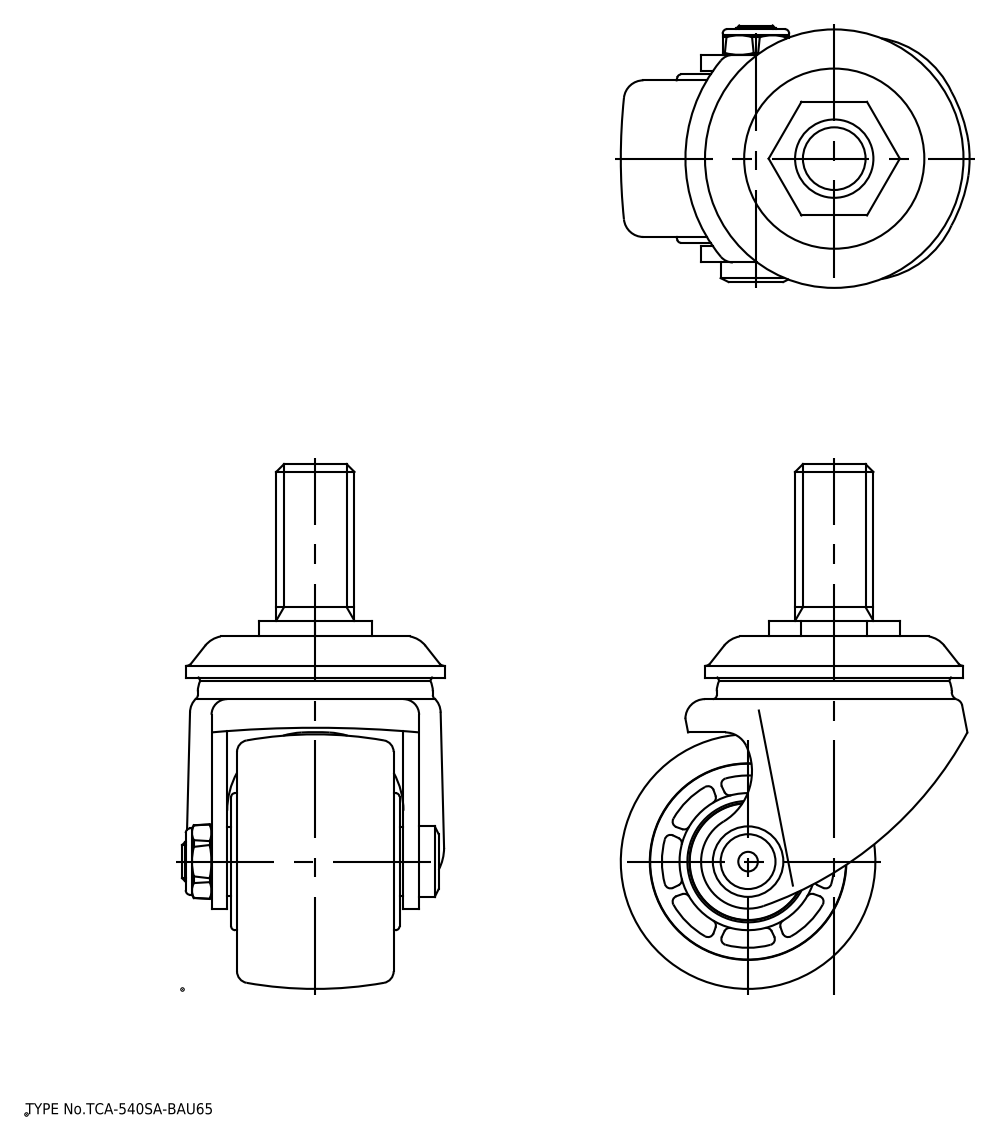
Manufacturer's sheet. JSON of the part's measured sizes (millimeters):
{"part_name": "wheel", "step_written_by": "spGate 19.8.4 (****-****-****-****) (AUTOMOTIVE_DESIGN)", "units": "millimeters", "bodies": {"solids": 2, "faces": 210, "planar": 57, "cylindrical": 87, "other": 66}, "overall_size": [134, 88.47, 69.5], "volume_mm3": 214094, "surface_area_mm2": 52502, "round_holes": [[30, 1], [50.2, 1], [54, 1]], "round_bosses_or_shafts": [[66, 1], [60, 1], [50, 1], [35, 1], [18, 1], [17.6, 1], [17, 1], [10, 1]], "partial_cylinders_radius": [[1.5, 32], [5, 3], [1, 1], [2, 1], [6, 1], [12, 1], [15, 1], [22, 1]], "face_to_face_distances": [42.5, 2.5, 4, 40, 6.5, 46.5, 49, 1, 1.5, 4.5]}
